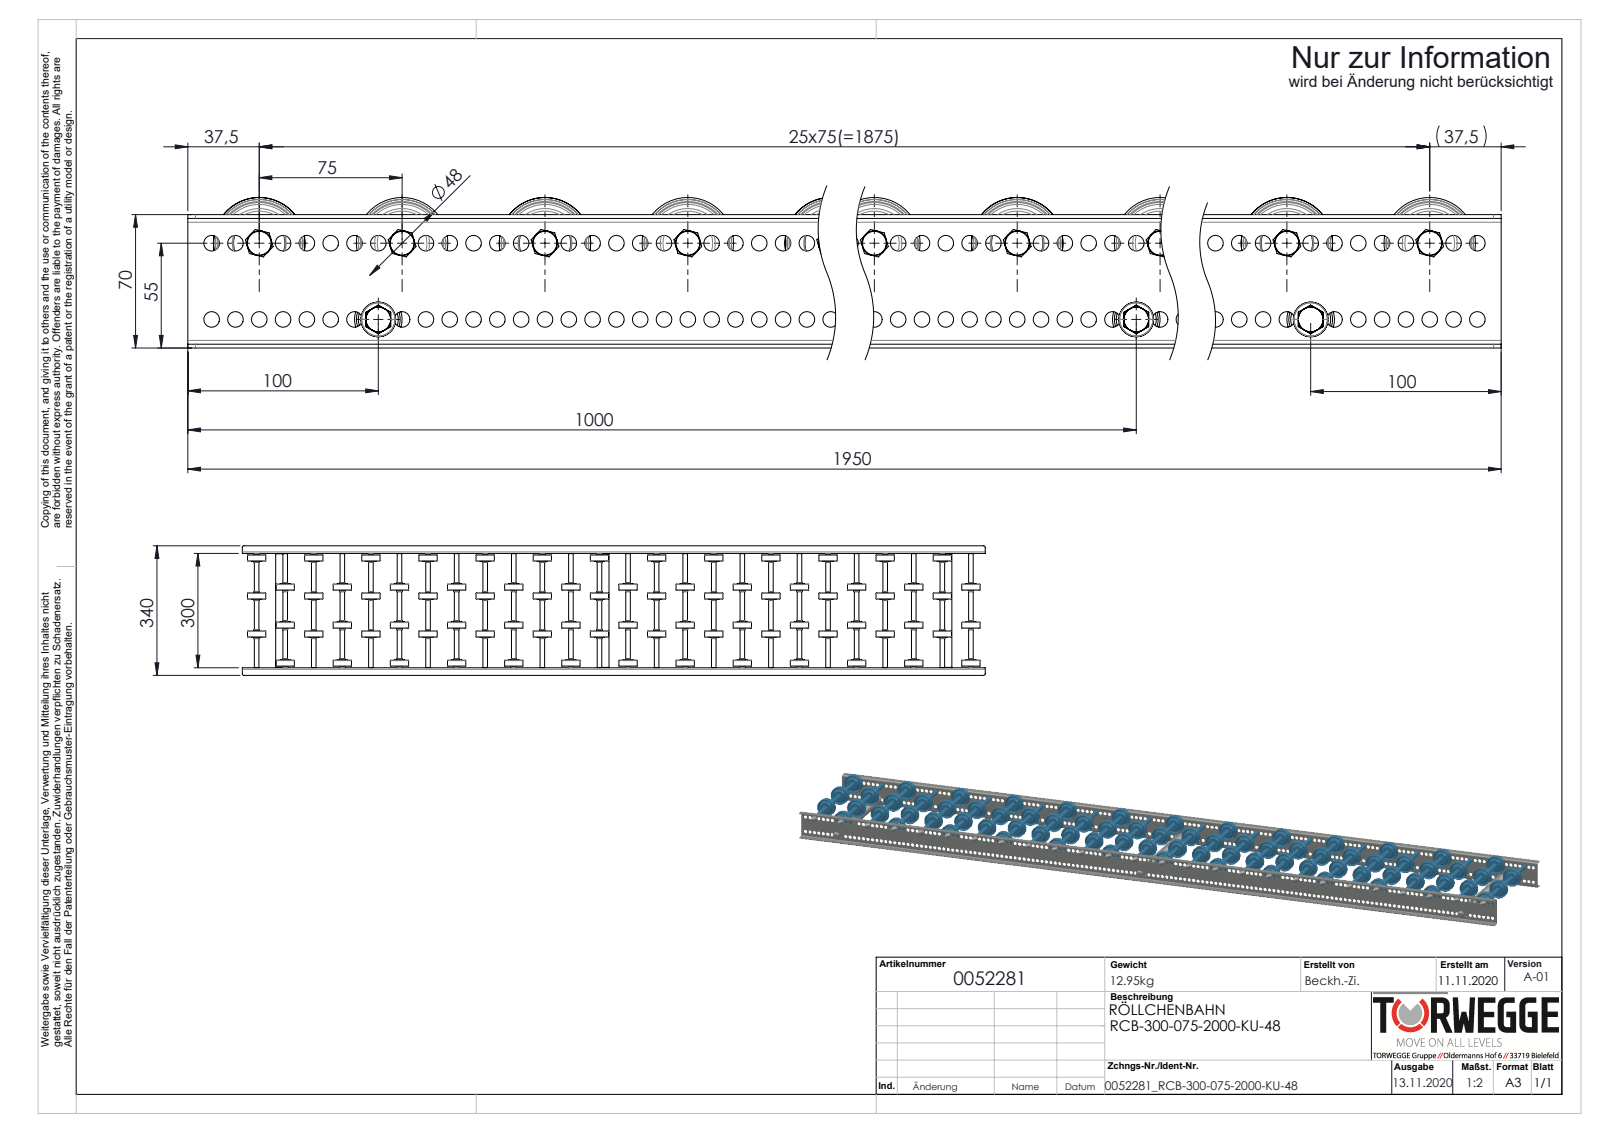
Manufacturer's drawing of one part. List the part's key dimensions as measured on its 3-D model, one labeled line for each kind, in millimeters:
Part name (STEP PRODUCT): Hutmutter_DIN_1587_M8; 0011532_2300-48-8; Röllchenachse-für-Konfiguration_EL300; 0046278_KB-ROHR-12X1,75mm_KFG_L76 (+5 more)
STEP written by: SolidWorks 2020 (AUTOMOTIVE_DESIGN)
Units: millimetres
Bodies: 251 solids, 9148 faces (1644 planar, 3292 cylindrical, 4212 other)
Overall size (bounding box): 1950 × 340 × 79
Volume: 3 110 000 mm³ · Surface area: 2 356 000 mm²
Round holes (diameter × count): ⌀8.2 ×310, ⌀6.65 ×26, ⌀9.65 ×26, ⌀13.7 ×26, ⌀6.8 ×3, ⌀21 ×3
Round bosses / shafts (diameter × count): ⌀8 ×29, ⌀48 ×26, ⌀27 ×26, ⌀12.7 ×26, ⌀12.5 ×26, ⌀12 ×26, ⌀25 ×3
Partial cylindrical surfaces — rounded edges, fillets, slot ends (radius × count): R4 ×8, R2 ×4
Main face-to-face distances: 2, 302, 68, 304, 300, 70, 66, 99.8, 16.3, 76.1
Hole centre spacings: 12.5, 25, 37.5, 50, 62.5, 75, 87.5, 100
